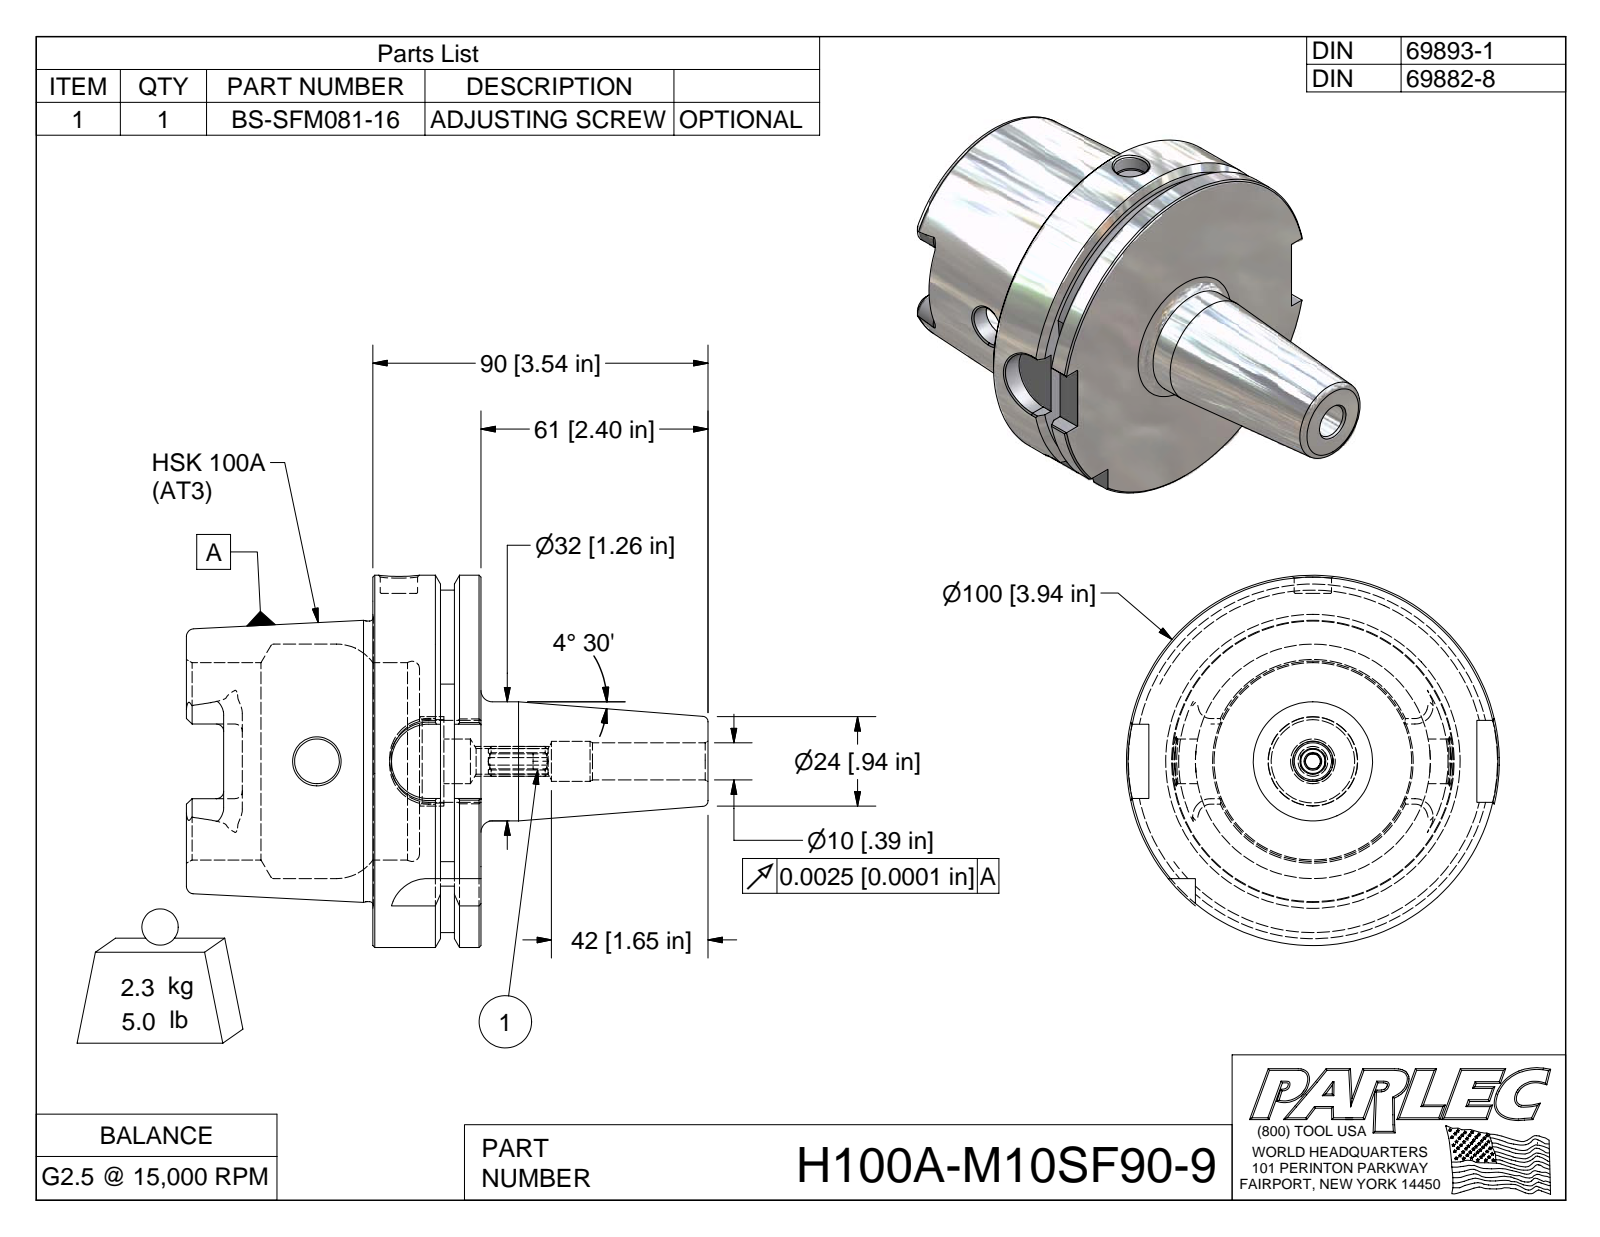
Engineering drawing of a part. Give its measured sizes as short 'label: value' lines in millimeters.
name: H100A-M10SF90-9; H100A-M10SF90-9-1; BS-SFM081-16
written by: Autodesk Inventor 2009 (AUTOMOTIVE_DESIGN)
unit: mm
bodies: 2 solids, 147 faces (48 planar, 29 cylindrical, 70 other)
size: 139.9 × 100 × 100
volume: 293 000 mm³; area: 56 790 mm²
holes: 1× ⌀10, 1× ⌀10, 1× ⌀10.7, 1× ⌀12, 1× ⌀22.4, 1× ⌀53, 1× ⌀63
bosses: 1× ⌀100, 1× ⌀75.4, 1× ⌀32
rounds: 4× R10, 3× R2, 2× R4.9, 1× R4, 1× R46
face distances: 29, 12.5, 16.5, 50, 62.5, 79, 68.1, 18.1, 5.6, 10.9
